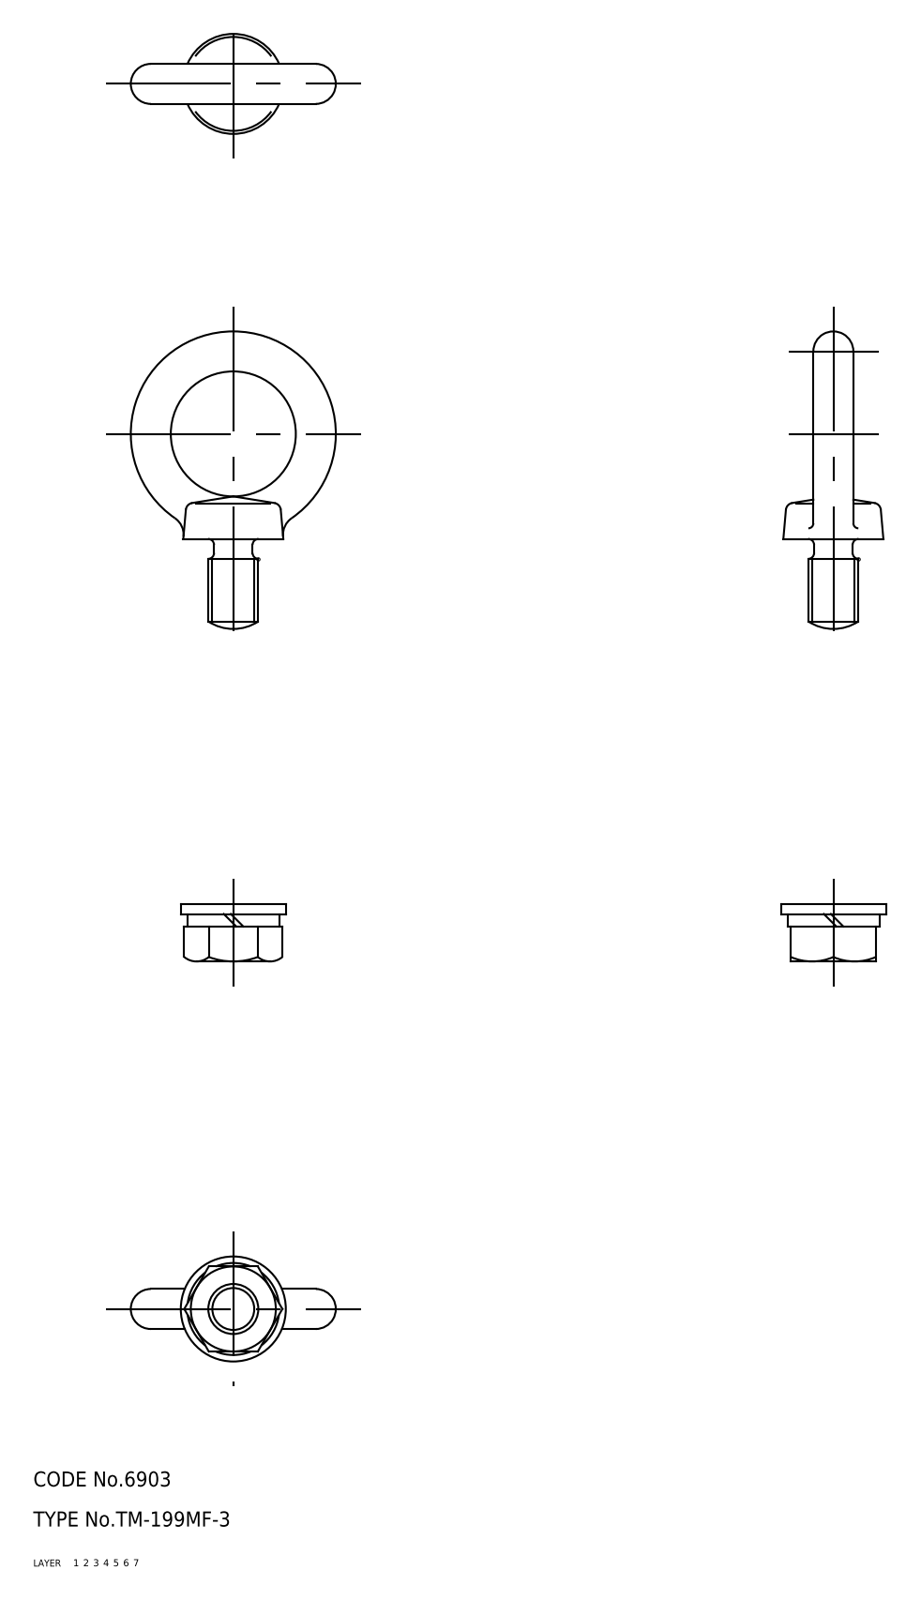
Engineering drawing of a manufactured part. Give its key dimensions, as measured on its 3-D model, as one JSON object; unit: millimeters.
{"part_name": "TM_199MF_3", "step_written_by": "SolidWorks 2003240 (AUTOMOTIVE_DESIGN)", "units": "millimeters", "bodies": {"solids": 4, "faces": 52, "planar": 13, "cylindrical": 12, "other": 27}, "overall_size": [59.5, 41, 21], "volume_mm3": 10204, "surface_area_mm2": 5920, "round_holes": [[10, 1]], "round_bosses_or_shafts": [[21, 1], [18.4, 1]], "face_to_face_distances": [2, 2.5, 4.5, 17, 7, 9.5, 11.5]}
